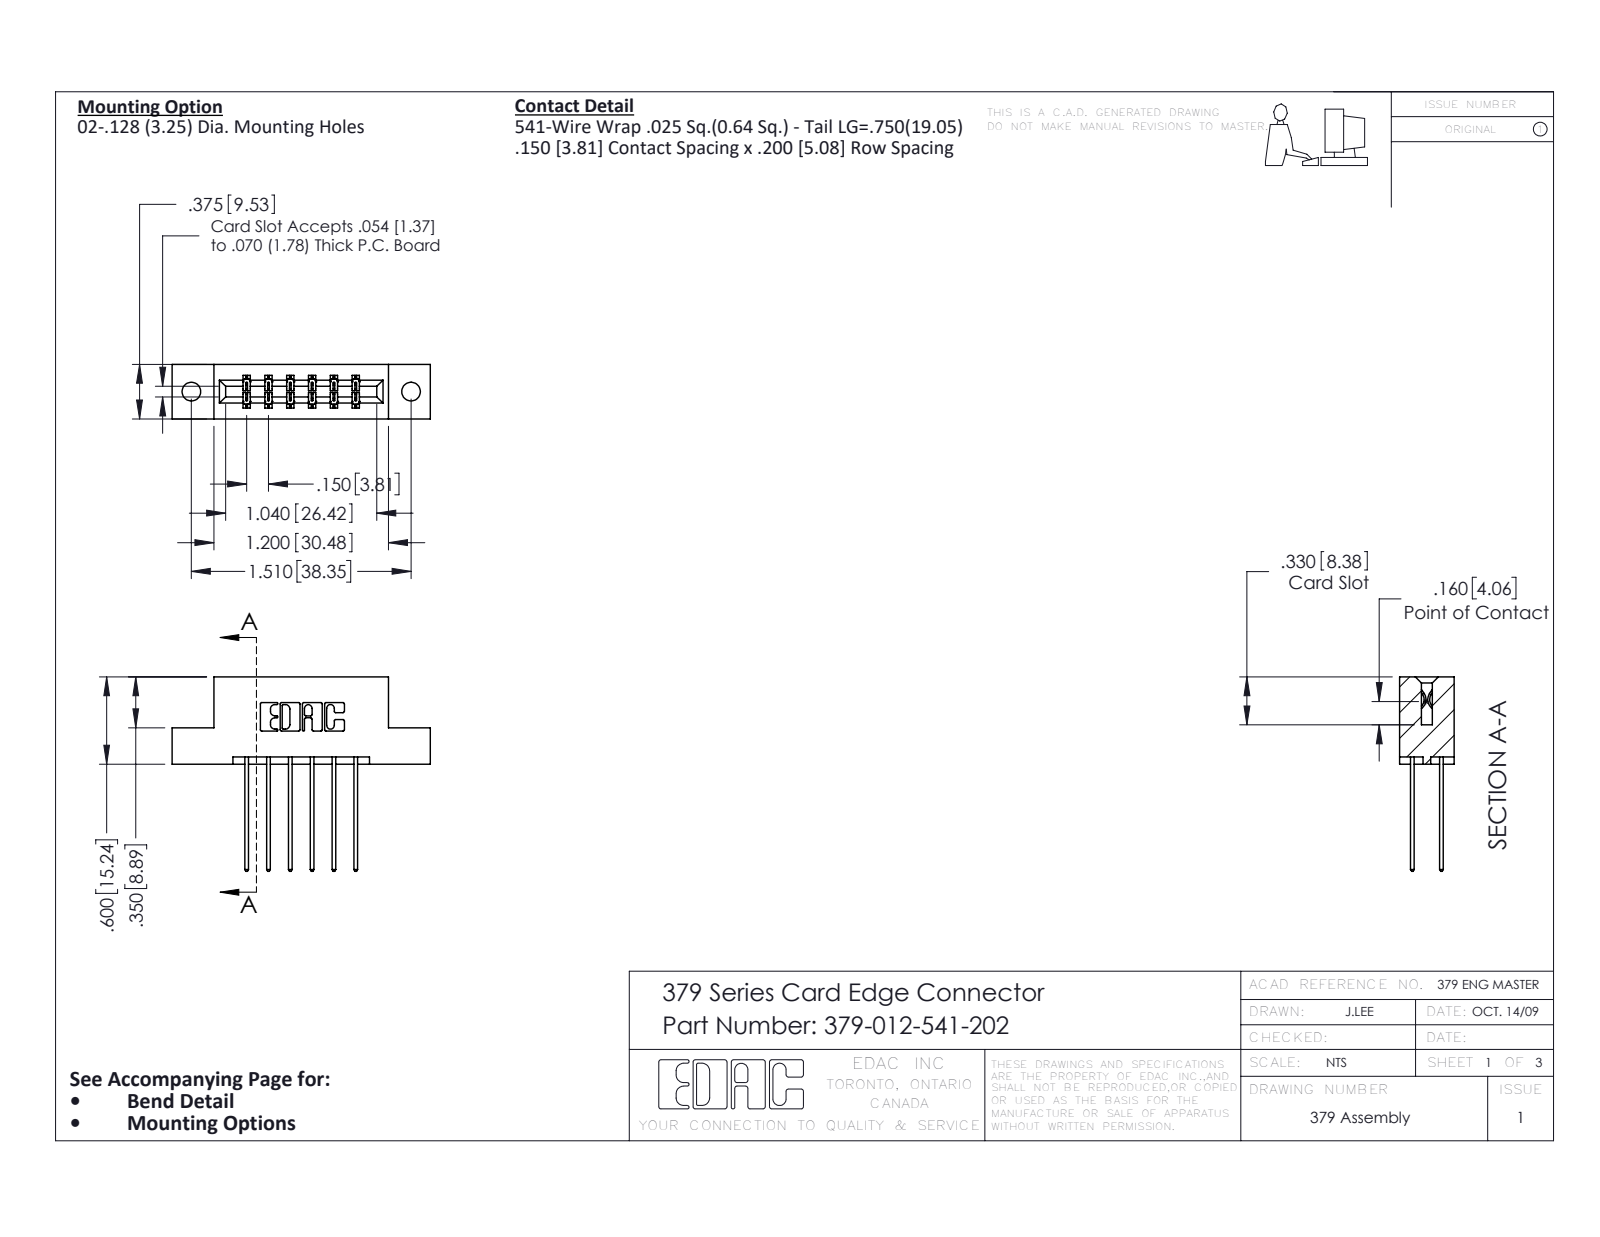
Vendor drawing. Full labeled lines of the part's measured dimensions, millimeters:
Part name (STEP PRODUCT): 379-012-541-202; 345-292-001_345-293-141; 379 Part_Flush - .128 Dia
STEP written by: SolidWorks 2016 (CONFIG_CONTROL_DESIGN)
Units: millimetres
Bodies: 13 solids, 738 faces (502 planar, 236 cylindrical, 0 other)
Overall size (bounding box): 45.1 × 34 × 9.5
Volume: 4 380 mm³ · Surface area: 4 661 mm²
Round holes (diameter × count): ⌀3.3 ×2
Partial cylindrical surfaces — rounded edges, fillets, slot ends (radius × count): R0.3 ×22, R0.2 ×18, R0.3 ×12, R0.2 ×6, R0.8 ×6, R0.7 ×3, R0.4 ×2, R0.6 ×2
Main face-to-face distances: 7.6, 5.1, 3.8, 2.5, 9.5, 1.3, 1.9, 6.4, 8.9, 14
Hole centre spacings: 38.4
